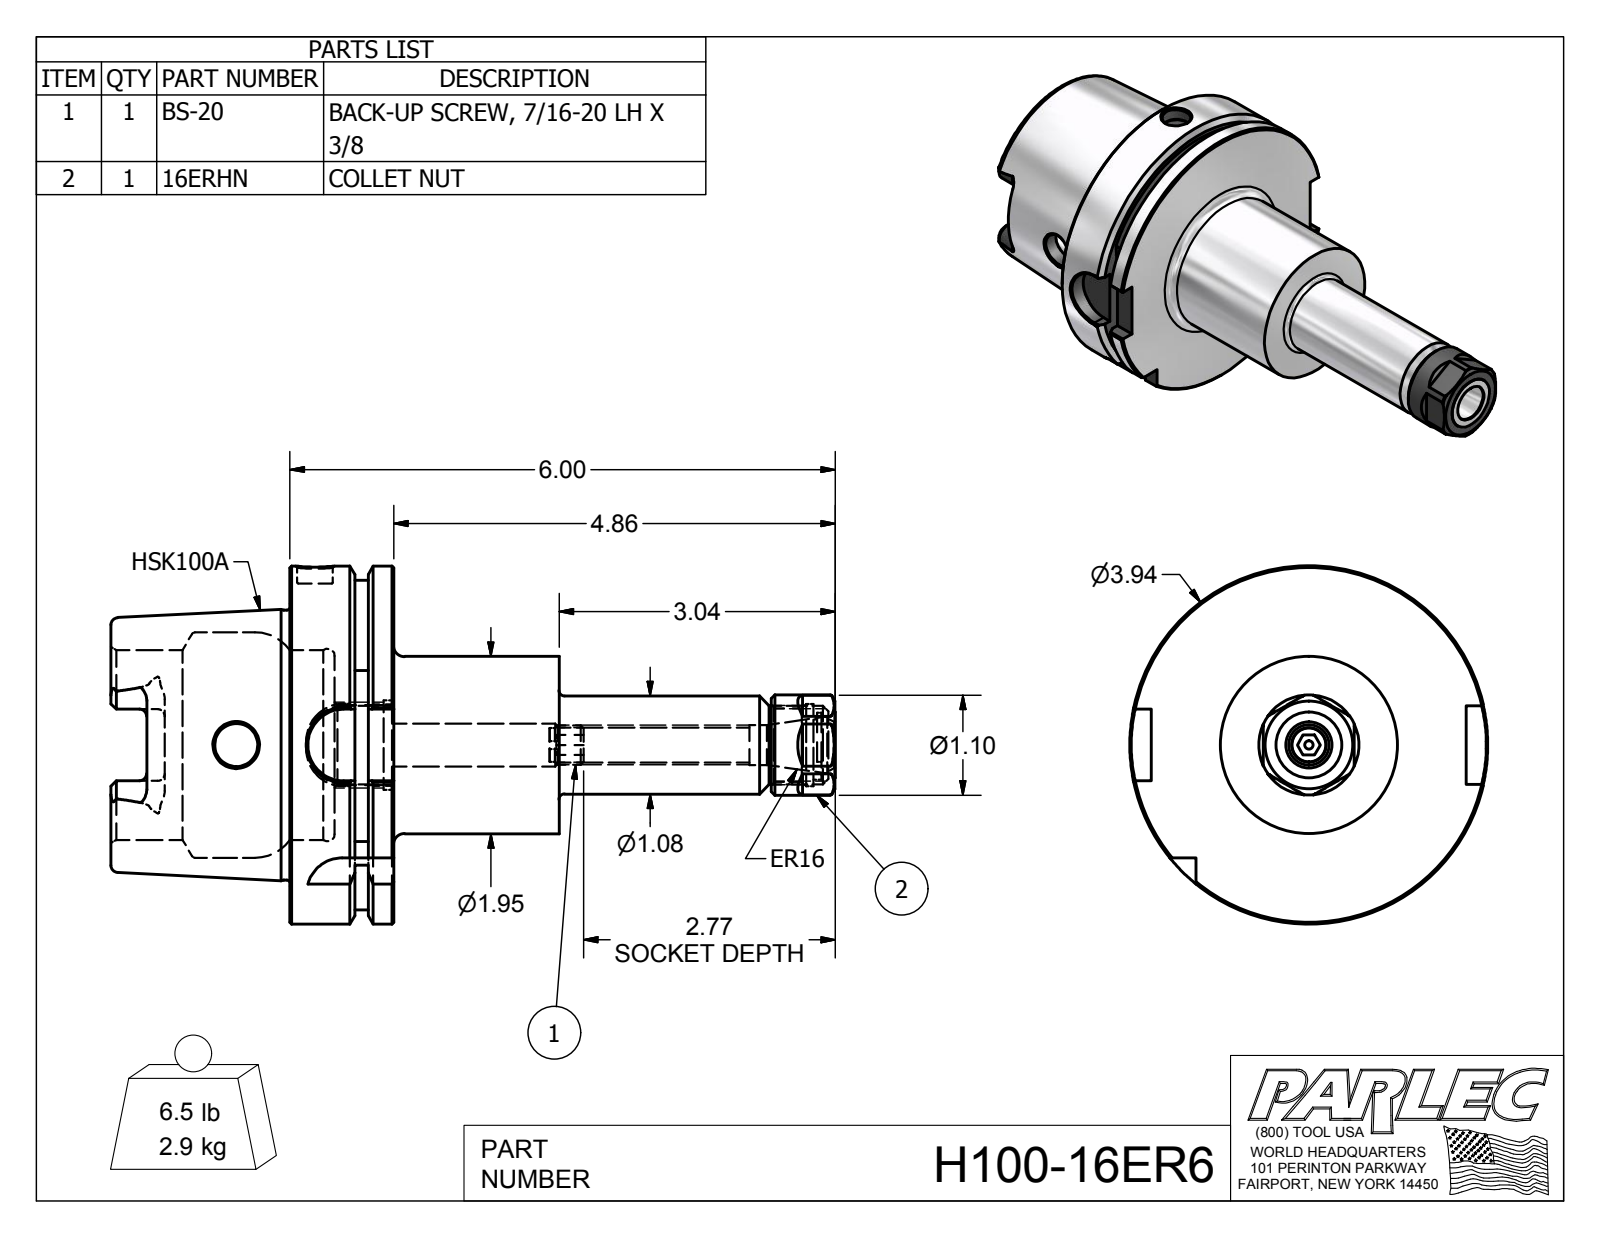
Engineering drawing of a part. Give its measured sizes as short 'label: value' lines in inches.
name: H100-16ER6; H100-16ER6-1; BS-20; 16ERHN
written by: Autodesk Inventor 2012 (AUTOMOTIVE_DESIGN)
unit: in
bodies: 3 solids, 184 faces (72 planar, 47 cylindrical, 65 other)
size: 7.969 × 3.937 × 3.937
volume: 23.02 in³; area: 110.4 in²
holes: 2× ⌀0.472, 1× ⌀0.09, 1× ⌀0.383, 1× ⌀0.394, 1× ⌀0.44, 1× ⌀0.472, 1× ⌀0.508, 1× ⌀0.661, 1× ⌀0.807, 1× ⌀0.881, 1× ⌀0.906, 1× ⌀0.985
bosses: 1× ⌀3.937, 1× ⌀2.967, 1× ⌀1.95, 1× ⌀1.102, 1× ⌀1.08, 1× ⌀0.866, 1× ⌀0.724, 1× ⌀0.432
rounds: 6× R0.079, 4× R0.192, 4× R0.394, 1× R0.354, 1× R1.811
face distances: 1.142, 0.492, 0.65, 2.962, 2.47, 1.82, 1.969, 2.461, 3.11, 4.93
hole spacings: 0.051
